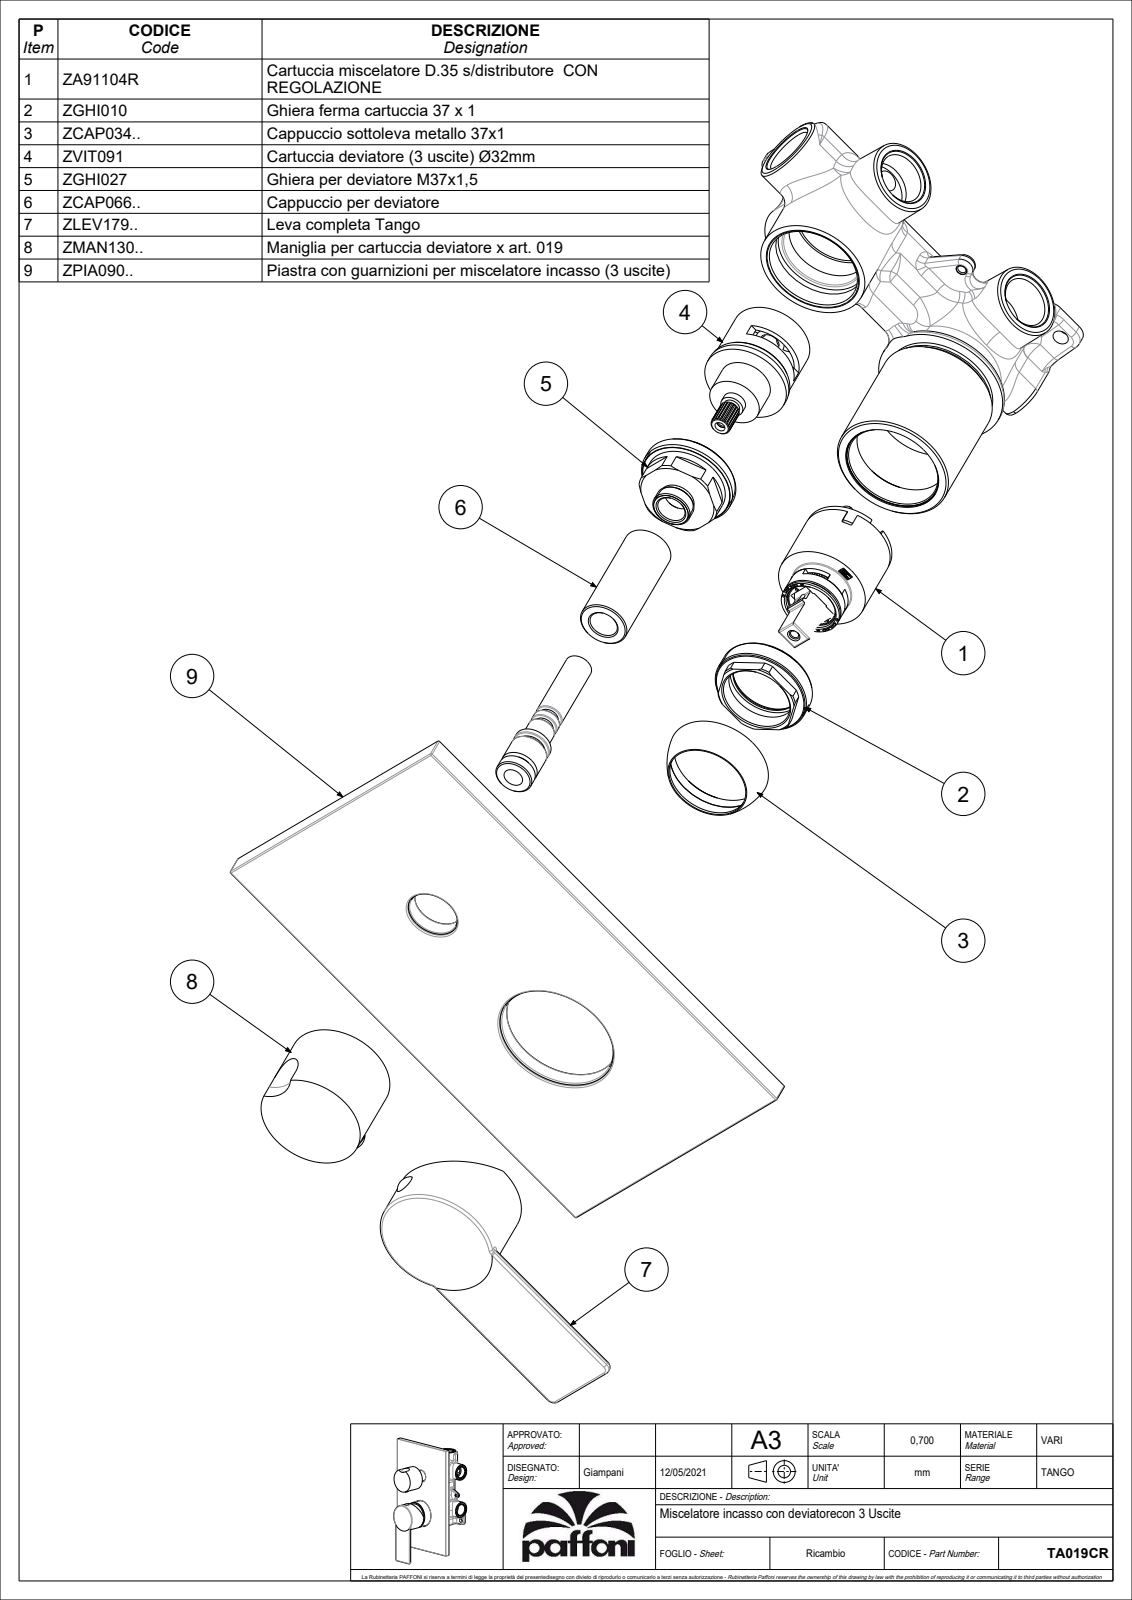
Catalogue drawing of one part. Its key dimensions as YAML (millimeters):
part_name: "TA018CR"
step_written_by: "CREO PARAMETRIC BY PTC INC, 2020044 (CONFIG_CONTROL_DESIGN)"
units: millimeters
bodies: {solids: 3, faces: 232, planar: 70, cylindrical: 90, other: 72}
overall_size: [204, 120, 56.25]
volume: 239123
surface_area: 84718
round_holes:
  - {diameter: 3, count: 2}
  - {diameter: 4.2, count: 2}
  - {diameter: 36, count: 2}
  - {diameter: 3.2, count: 1}
  - {diameter: 11, count: 1}
  - {diameter: 14.8, count: 1}
  - {diameter: 30.6, count: 1}
  - {diameter: 37.5, count: 1}
round_bosses_or_shafts:
  - {diameter: 7.6, count: 2}
  - {diameter: 5.5, count: 2}
  - {diameter: 45.5, count: 1}
  - {diameter: 44.8, count: 1}
  - {diameter: 40, count: 1}
  - {diameter: 24, count: 1}
  - {diameter: 18.7, count: 1}
partial_cylinders:
  - {radius: 0.5, count: 10}
  - {radius: 1, count: 6}
  - {radius: 1.5, count: 4}
  - {radius: 3, count: 2}
  - {radius: 3.5, count: 1}
  - {radius: 12.5, count: 1}
face_to_face_distances: [8, 54.6, 46.6, 3, 51.6, 43.6, 120, 3.5, 0.5, 51.1]
hole_center_spacings: [1.8, 10, 68, 78]
